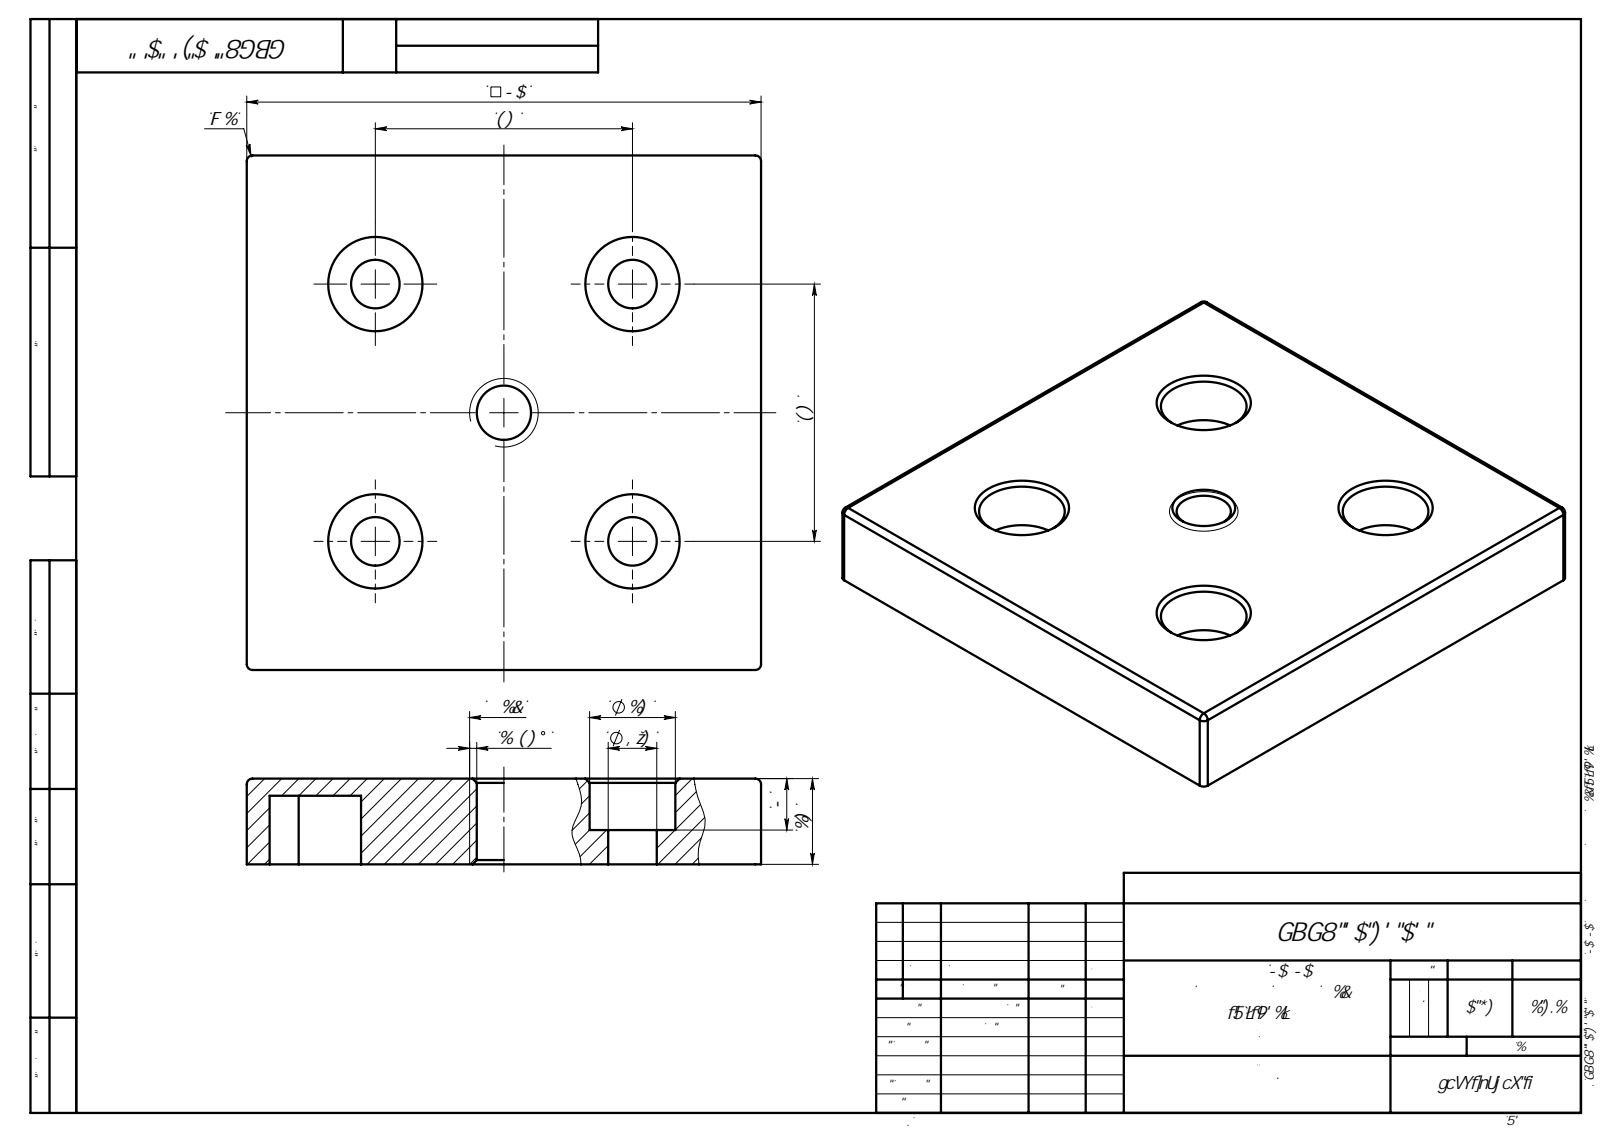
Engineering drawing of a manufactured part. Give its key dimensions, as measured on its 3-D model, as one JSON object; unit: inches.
{"step_written_by": "SolidWorks 2014 (AUTOMOTIVE_DESIGN)", "units": "inches", "bodies": {"solids": 1, "faces": 115, "planar": 46, "cylindrical": 53, "other": 16}, "overall_size": [3.543, 3.543, 0.591], "volume_in3": 5.102, "surface_area_in2": 47.6, "round_holes": [[0.335, 4], [0.591, 4], [0.374, 1]], "partial_cylinders_radius": [[0.039, 16], [0.551, 4], [0.984, 1]], "face_to_face_distances": [0.591, 0.157, 3.386, 3.543, 0.472, 0.118, 3.228, 0.236, 0.728, 2.815], "hole_center_spacings": [1.253, 1.772, 2.506]}
